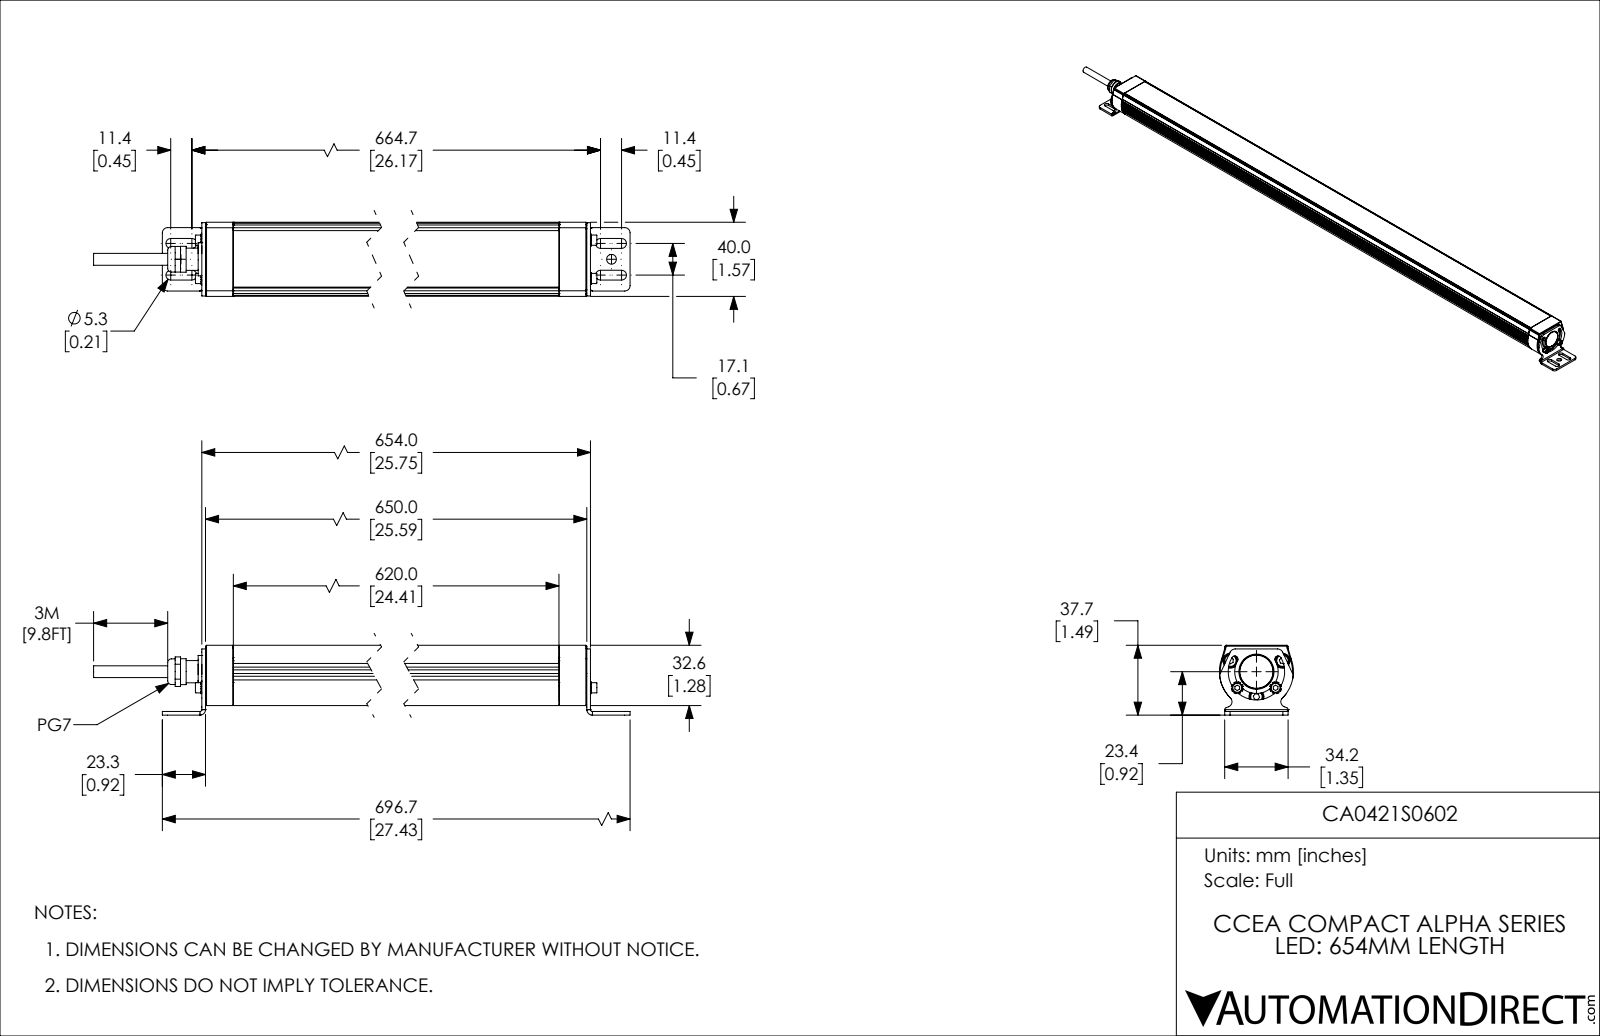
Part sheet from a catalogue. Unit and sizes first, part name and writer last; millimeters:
Units: millimetres
Overall size (bounding box): 733.73 × 40 × 37.73
Round holes (diameter × count): ⌀2 ×4, ⌀3.3 ×3, ⌀4.5 ×3, ⌀7.5 ×3, ⌀2.5 ×2, ⌀3.2 ×2, ⌀5.3 ×2, ⌀8.5 ×1, ⌀11.5 ×1, ⌀12 ×1, ⌀14 ×1, ⌀19 ×1
Round bosses / shafts (diameter × count): ⌀1 ×4, ⌀7 ×3, ⌀4 ×3, ⌀5.5 ×2, ⌀3 ×2, ⌀18.3 ×1, ⌀15 ×1, ⌀13.86 ×1
Partial cylindrical surfaces — rounded edges, fillets, slot ends (radius × count): R0.25 ×56, R1 ×22, R3 ×22, R2.65 ×8, R2.85 ×6, R5.5 ×6, R1.5 ×4, R0.3 ×2
Main face-to-face distances: 2, 4.01, 0.5, 4.51, 2.5, 6.51, 25.98, 27.98, 28.48, 32.49
Hole centre spacings: 13.5, 1, 4.68, 5.63, 11.41, 13.07, 13.16, 15.09
Volume: 351 831 mm³ · Surface area: 261 527 mm²
Bodies: 22 solids, 1182 faces (392 planar, 577 cylindrical, 213 other)
Part name (STEP PRODUCT): CA0421S0602
STEP written by: SolidWorks 2021 (CONFIG_CONTROL_DESIGN)
